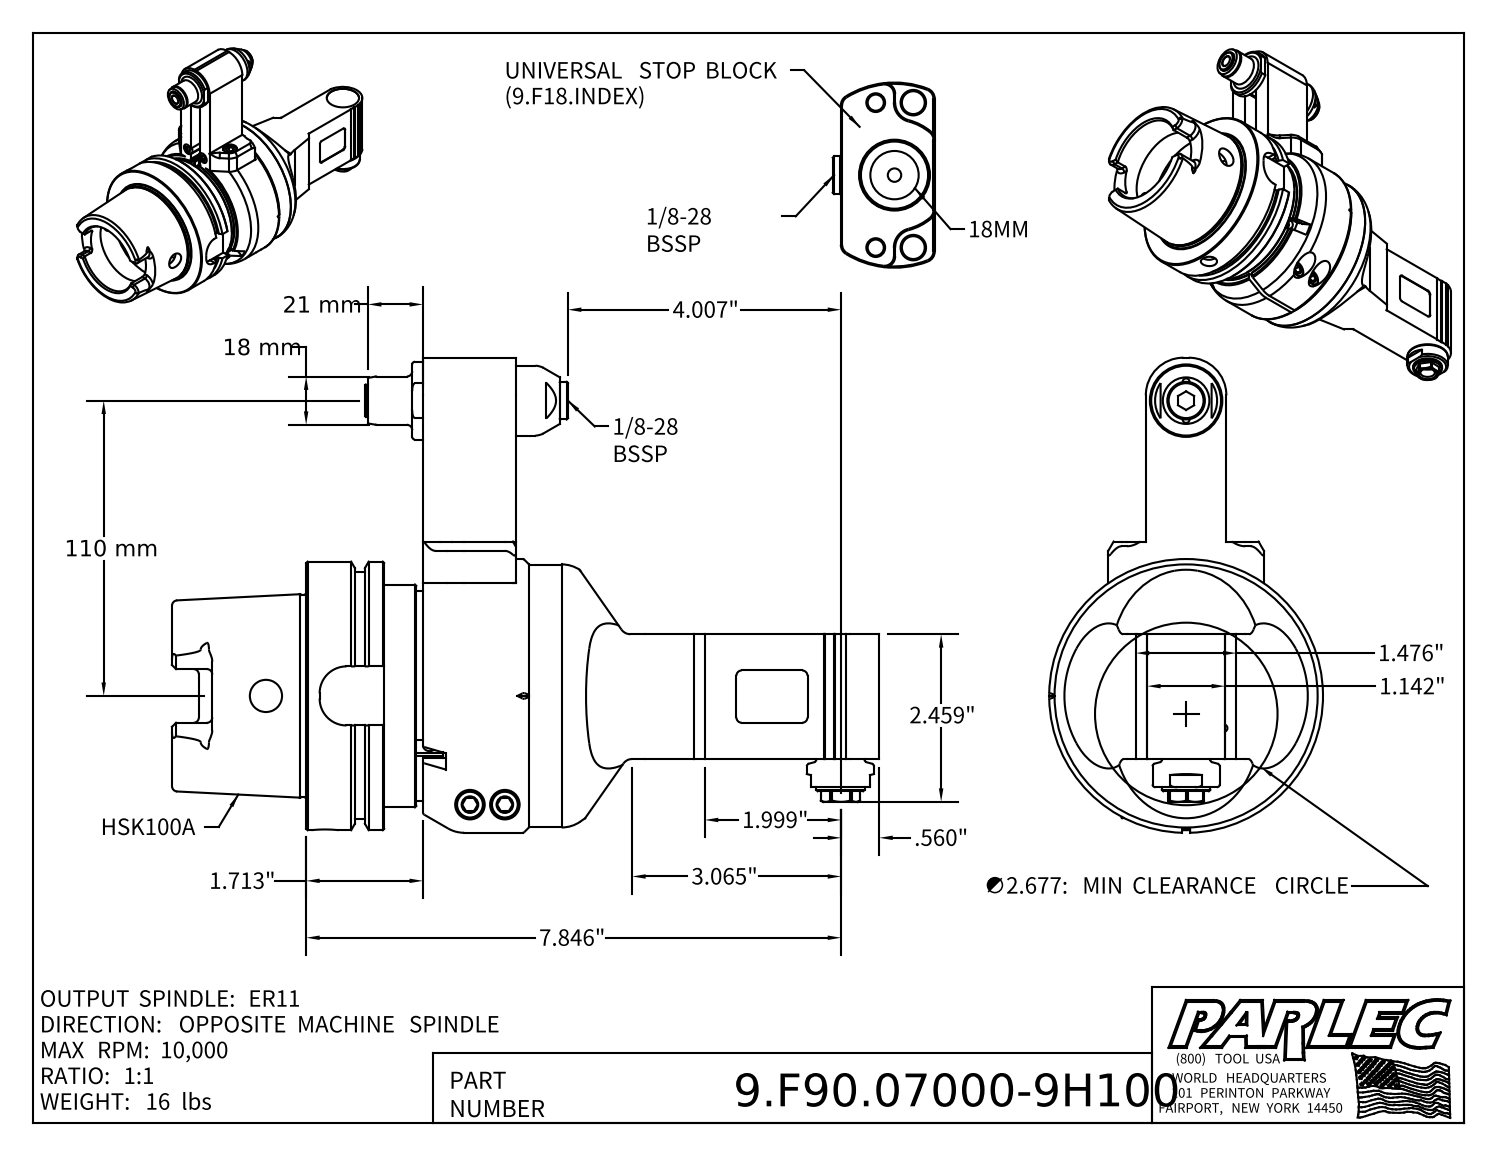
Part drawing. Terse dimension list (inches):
name: 9.F90.07000-9H100
written by: Autodesk Inventor 2022 (AUTOMOTIVE_DESIGN)
unit: in
bodies: 2 solids, 575 faces (270 planar, 174 cylindrical, 131 other)
size: 10.374 × 6.968 × 4.016
volume: 65.4 in³; area: 215.6 in²
holes: 3× ⌀0.197, 3× ⌀0.256, 2× ⌀0.102, 2× ⌀0.13, 2× ⌀0.165, 2× ⌀0.315, 2× ⌀0.335, 2× ⌀0.409, 2× ⌀0.433, 2× ⌀0.492, 2× ⌀1.063, 1× ⌀0.098
bosses: 4× ⌀0.394, 3× ⌀0.709, 2× ⌀0.472, 2× ⌀0.315, 2× ⌀0.236, 2× ⌀0.098, 1× ⌀4.016, 1× ⌀3.937
rounds: 18× R0.079, 14× R0.039, 6× R0.118, 5× R0.157, 4× R0.192, 4× R0.394, 2× R0.02, 2× R0.315
face distances: 1.142, 1.161, 0.02, 0.65, 1.555, 1.713, 0.335, 0.768, 1.831, 0.394
hole spacings: 0.276, 1.994, 2.11, 2.383, 2.657, 3.498, 0.014, 0.512
